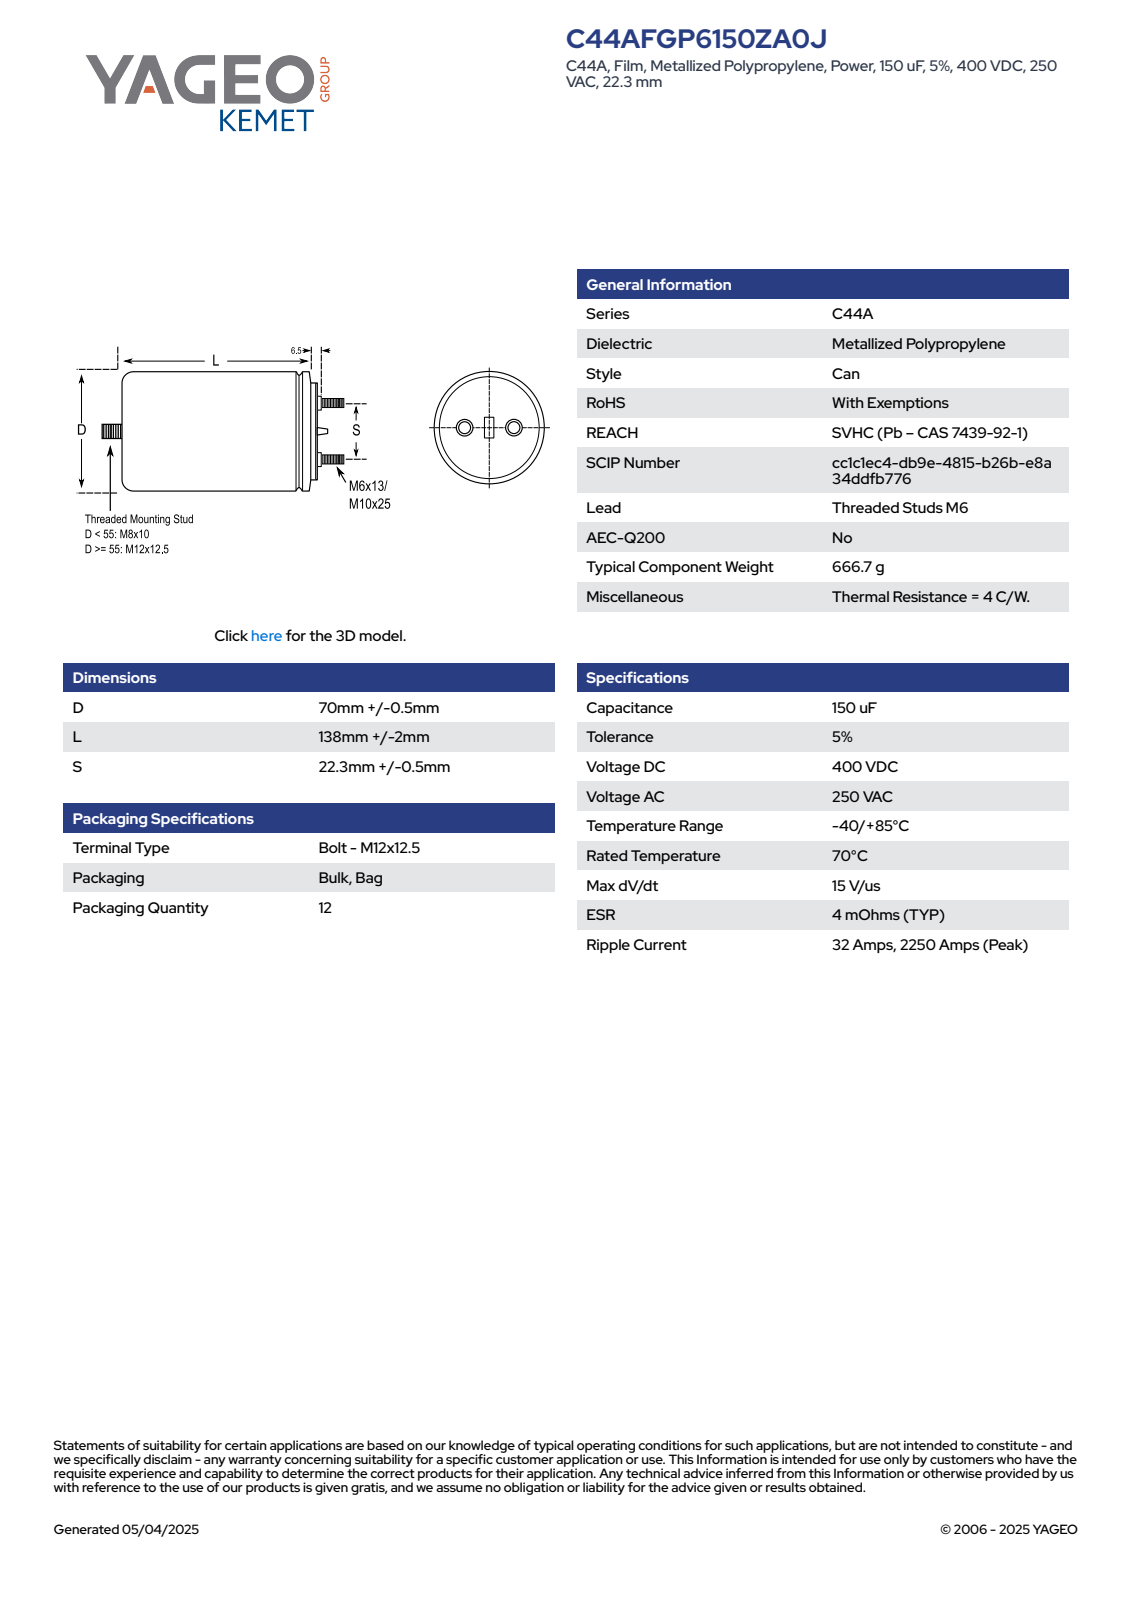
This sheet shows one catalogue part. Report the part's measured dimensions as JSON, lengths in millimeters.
{"part_name": "CFP_C44A_70X138_D70.5L140S22.3", "step_written_by": "SolidWorks 2014 (AUTOMOTIVE_DESIGN)", "units": "millimeters", "bodies": {"solids": 1, "faces": 102, "planar": 29, "cylindrical": 34, "other": 39}, "overall_size": [172, 70.5, 70.5], "volume_mm3": 556507, "surface_area_mm2": 40334, "round_bosses_or_shafts": [[9, 2], [6, 2], [70.5, 1], [55.29, 1], [12, 1]], "partial_cylinders_radius": [[35.24, 1]], "face_to_face_distances": [145, 12.5, 157.5, 159, 146.5, 1.5, 172, 159.5, 14.5, 13]}
